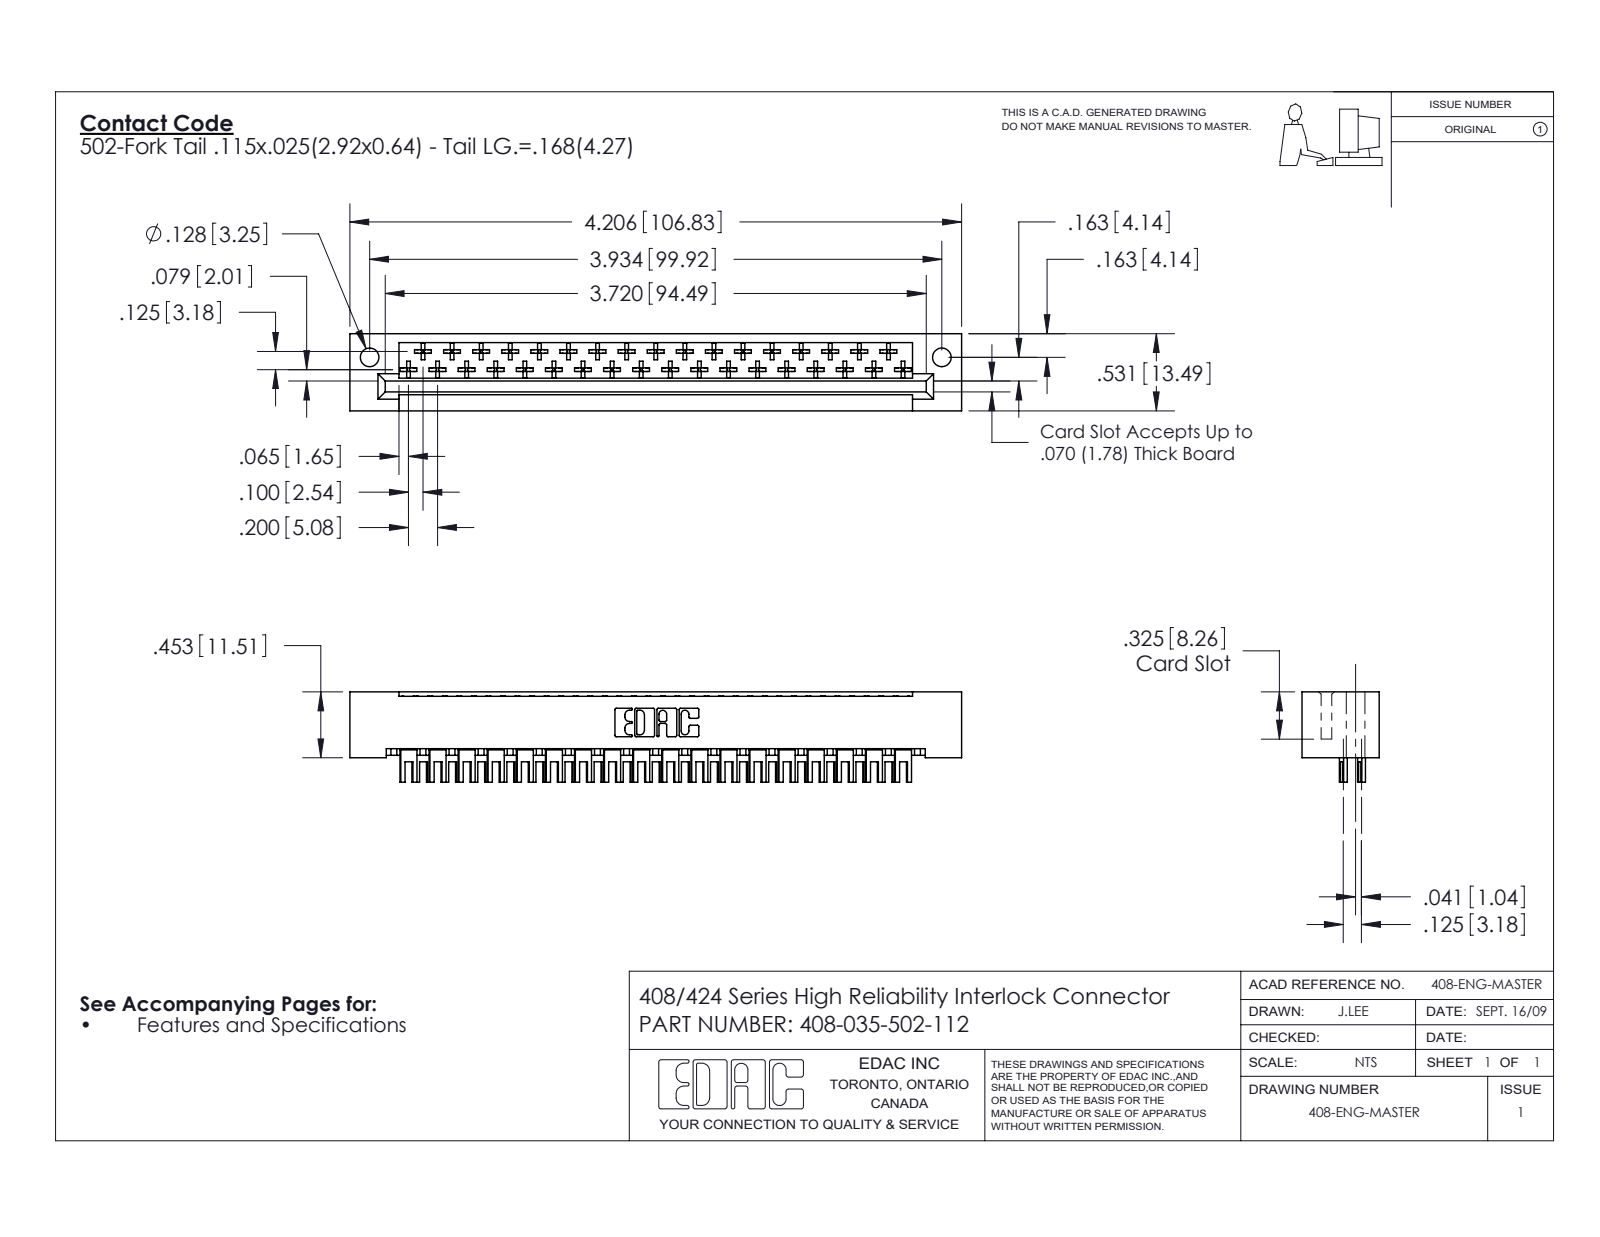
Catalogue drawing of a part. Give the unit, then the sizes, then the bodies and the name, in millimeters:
Units: millimetres
Overall size (bounding box): 106.8 × 15.8 × 13.5
Round holes (diameter × count): ⌀3.3 ×2
Partial cylindrical surfaces — rounded edges, fillets, slot ends (radius × count): R0.3 ×210, R0.5 ×37, R0.3 ×22, R0.2 ×6, R0.8 ×6, R0.7 ×3
Main face-to-face distances: 13.5, 0.6, 2.5, 3.2, 0.6, 10.2, 6, 6.6, 6.9, 7.5
Hole centre spacings: 99.9
Volume: 12 300 mm³ · Surface area: 14 870 mm²
Bodies: 36 solids, 1982 faces (1514 planar, 328 cylindrical, 140 other)
Part name (STEP PRODUCT): 408-035-502-112; 408 Part_035 - 1; 408-290-001_408-290-102
STEP written by: SolidWorks 2016 (CONFIG_CONTROL_DESIGN)
